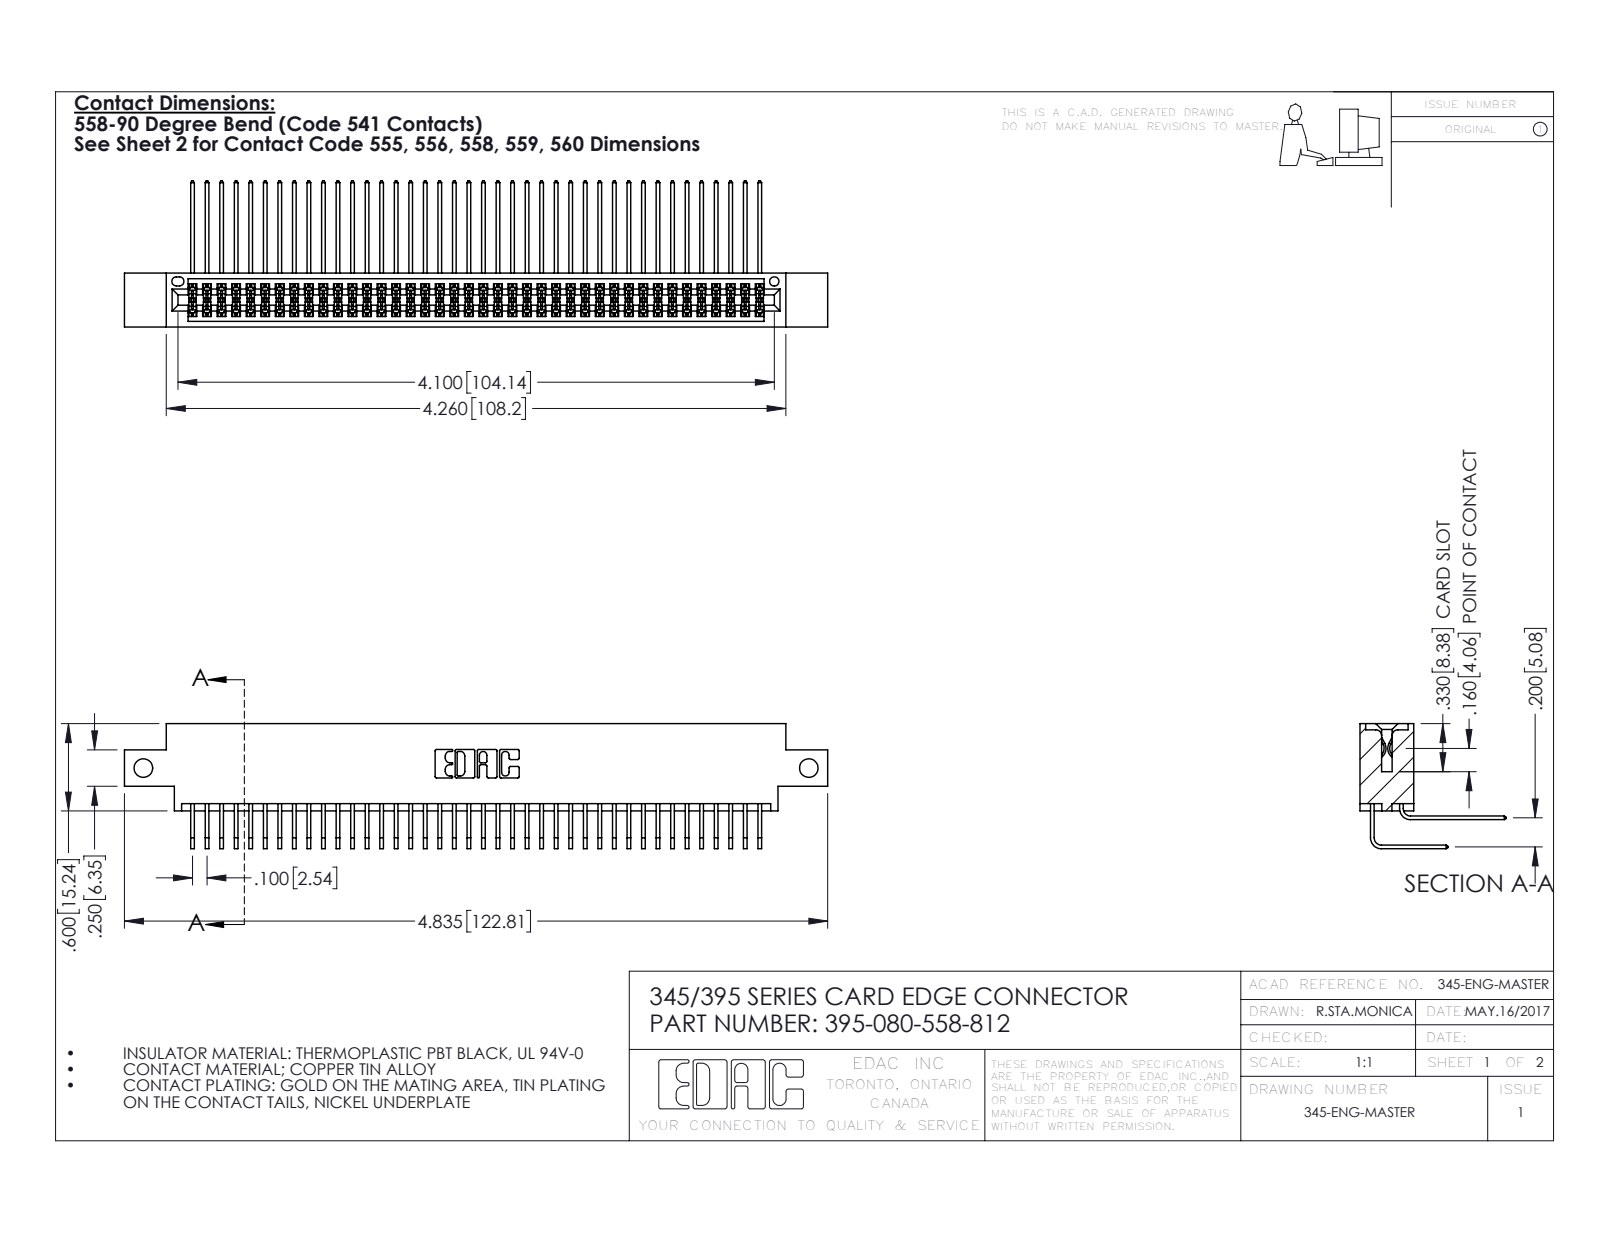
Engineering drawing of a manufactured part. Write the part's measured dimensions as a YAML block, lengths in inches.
part_name: "395-080-558-812; 345 Part_0.170 Offset - Side Mount; 345-292-001_558 Tail - 2; 345-292-001_558 559 Tail - 1"
step_written_by: "SolidWorks 2016 (CONFIG_CONTROL_DESIGN)"
units: inches
bodies: {solids: 81, faces: 4290, planar: 2884, cylindrical: 1406, other: 0}
overall_size: [4.835, 1.005, 0.859]
volume: 0.743
surface_area: 31.2
round_holes:
  - {diameter: 0.128, count: 2}
  - {diameter: 0.064, count: 1}
partial_cylinders:
  - {radius: 0.006, count: 121}
  - {radius: 0.01, count: 22}
  - {radius: 0.007, count: 6}
  - {radius: 0.031, count: 6}
  - {radius: 0.026, count: 3}
  - {radius: 0.014, count: 2}
  - {radius: 0.019, count: 2}
  - {radius: 0.022, count: 2}
face_to_face_distances: [0.072, 0.298, 0.2, 0.37, 0.098, 0.272, 0.025, 0.225, 0.175, 0.025]
hole_center_spacings: [4.575]
